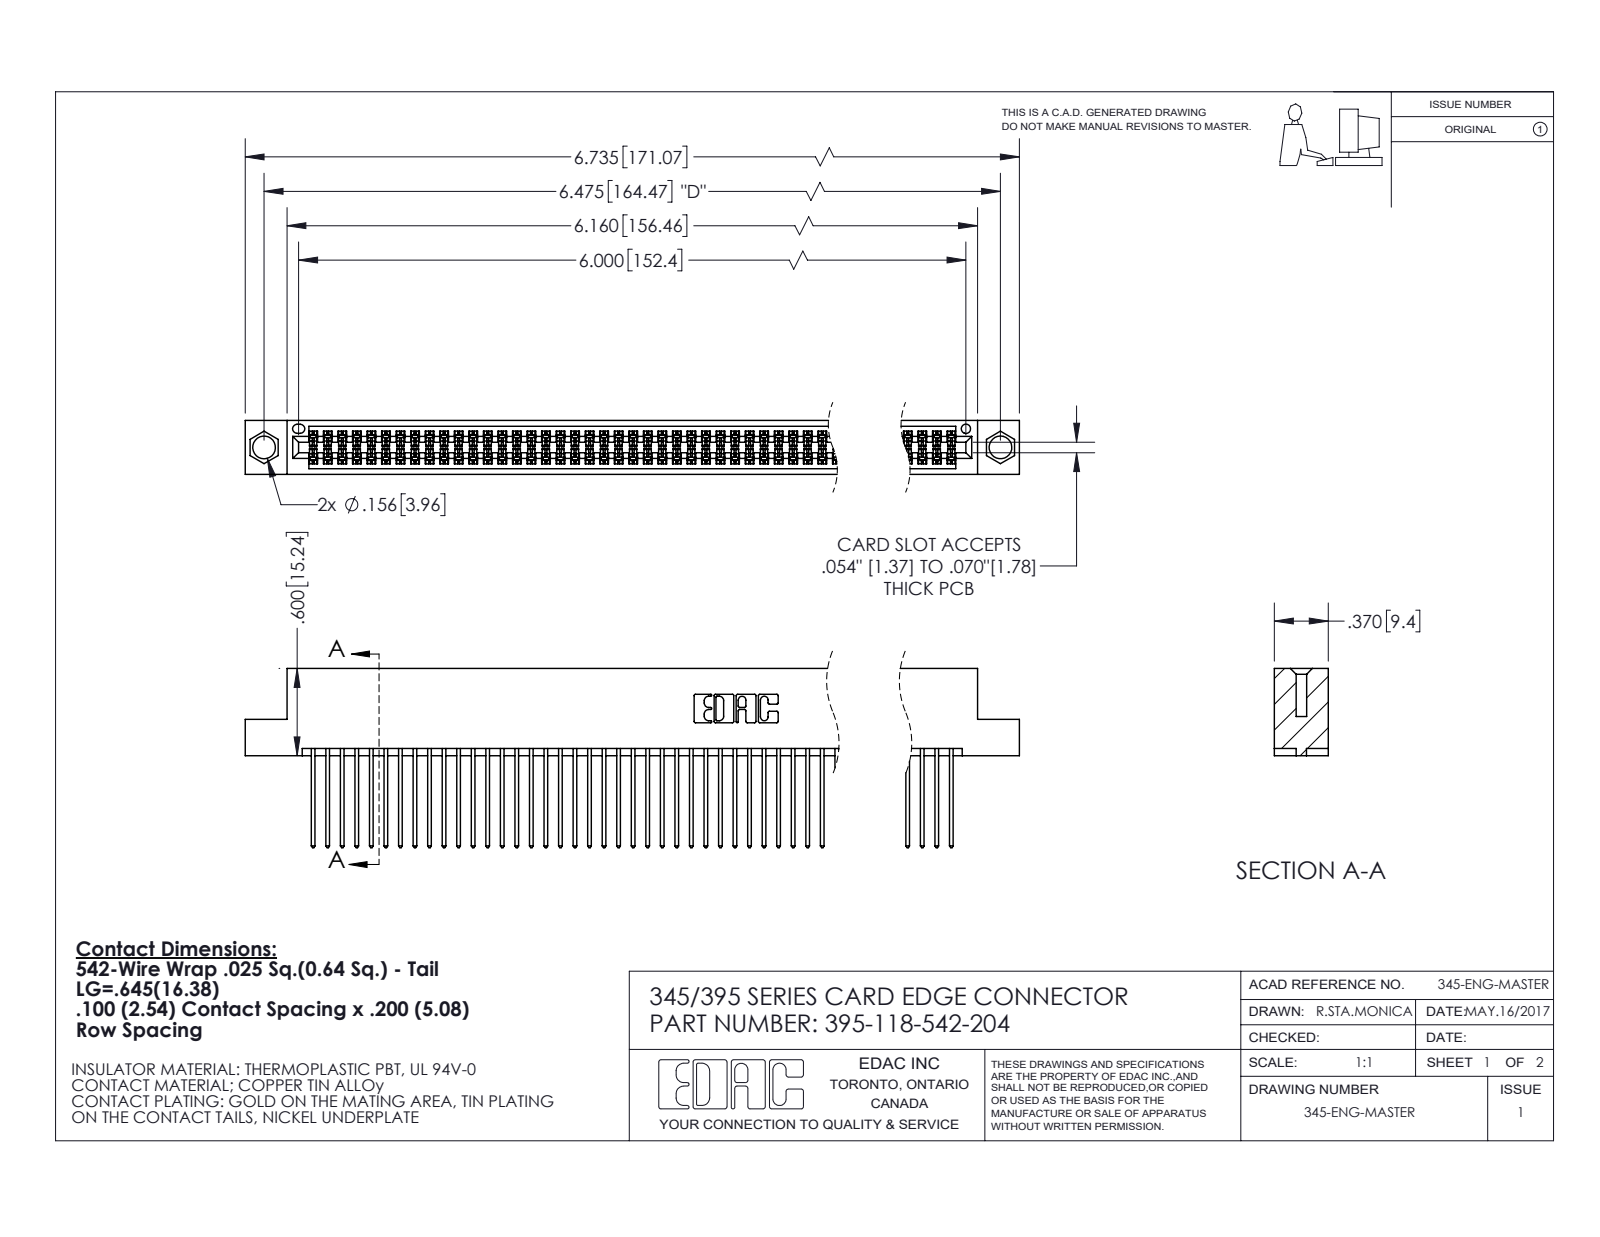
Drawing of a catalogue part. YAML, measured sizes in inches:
part_name: "395-118-542-204; 345 Part_Flush Mounting Lugs - 0.156 Dia-TI; 345-292-001_345-293-142"
step_written_by: "SolidWorks 2020 (CONFIG_CONTROL_DESIGN)"
units: inches
bodies: {solids: 119, faces: 6040, planar: 3988, cylindrical: 2052, other: 0}
overall_size: [6.735, 1.232, 0.37]
volume: 1.051
surface_area: 43.72
round_holes:
  - {diameter: 0.156, count: 2}
  - {diameter: 0.064, count: 1}
partial_cylinders:
  - {radius: 0.006, count: 177}
  - {radius: 0.01, count: 118}
  - {radius: 0.01, count: 22}
  - {radius: 0.007, count: 6}
  - {radius: 0.031, count: 6}
  - {radius: 0.026, count: 3}
  - {radius: 0.014, count: 2}
  - {radius: 0.019, count: 2}
face_to_face_distances: [0.072, 0.298, 0.2, 0.098, 0.272, 0.025, 0.225, 0.37, 0.175, 0.149]
hole_center_spacings: [0.27, 6.239, 6.475]
